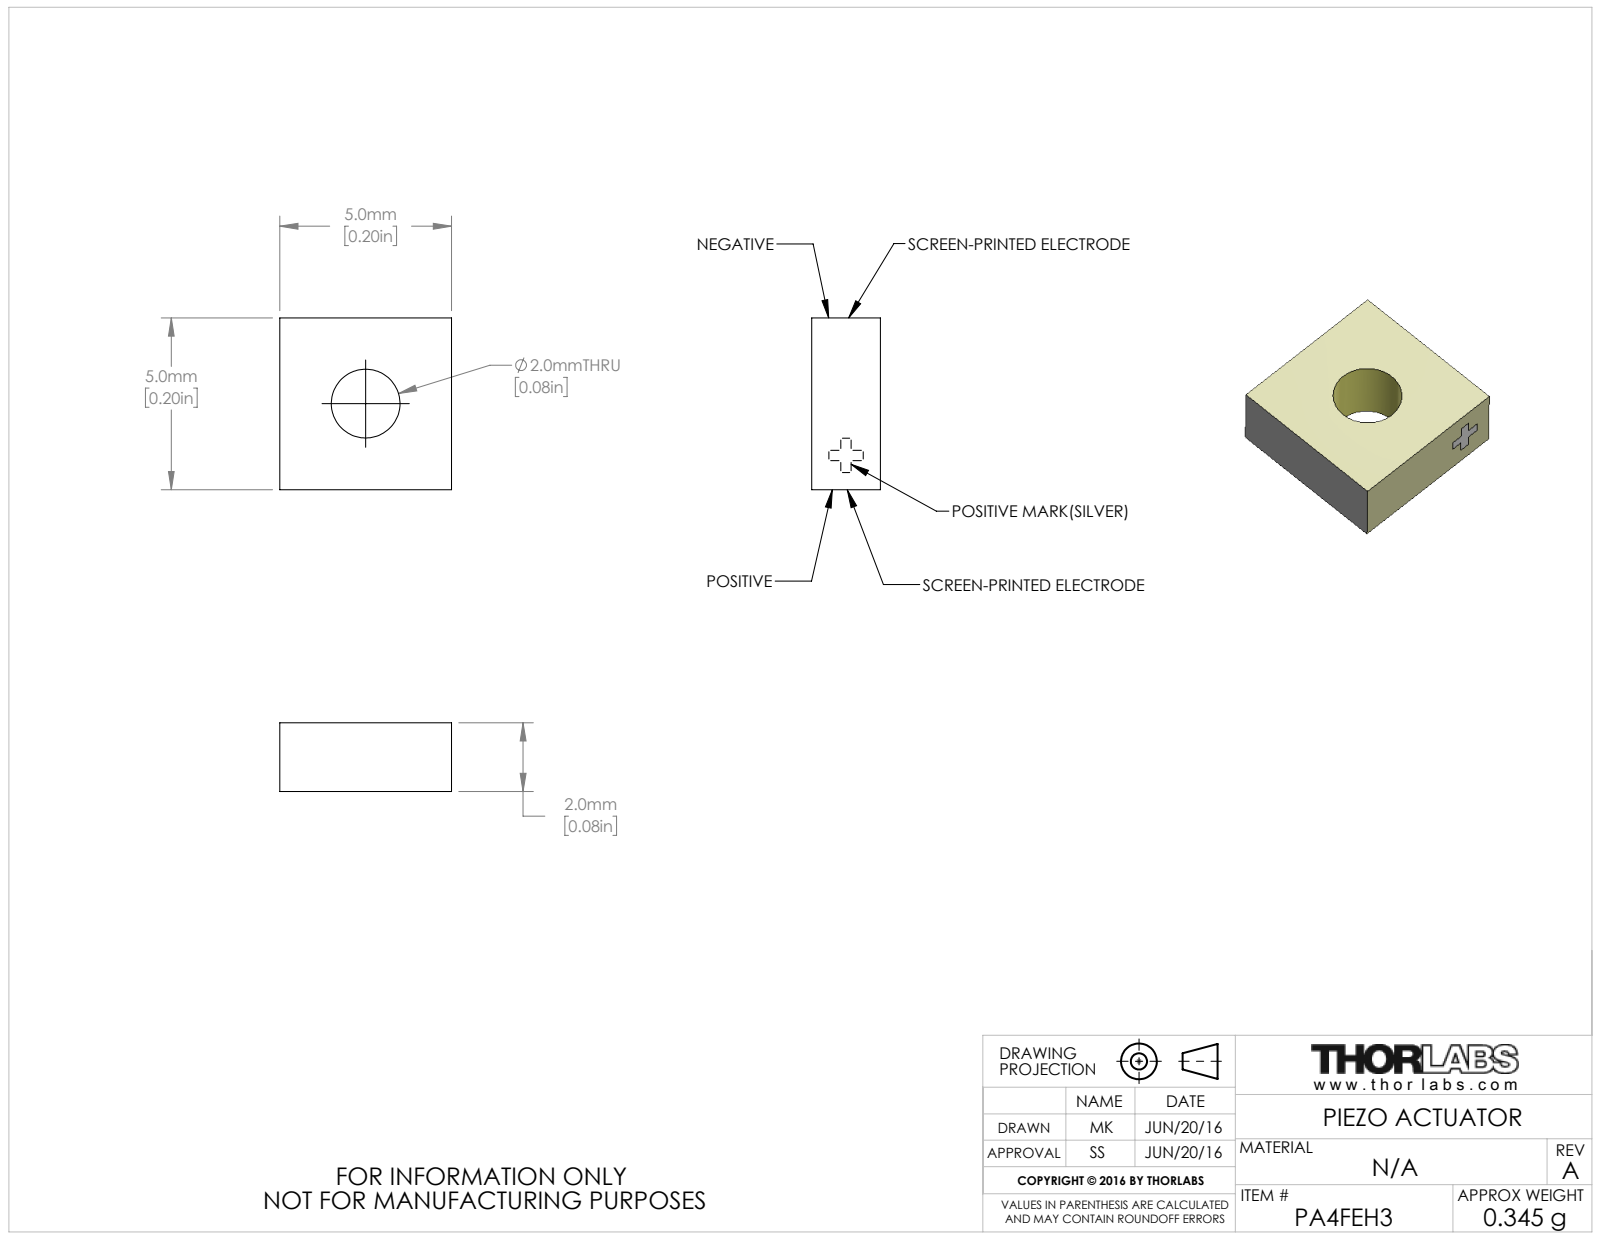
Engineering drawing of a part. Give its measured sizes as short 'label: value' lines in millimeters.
name: CTN008935
written by: SolidWorks 2016 (AUTOMOTIVE_DESIGN)
unit: mm
bodies: 1 solid, 9 faces (7 planar, 2 cylindrical, 0 other)
size: 5 × 5 × 2
volume: 44 mm³; area: 96 mm²
holes: 1× ⌀2
face distances: 2, 5
